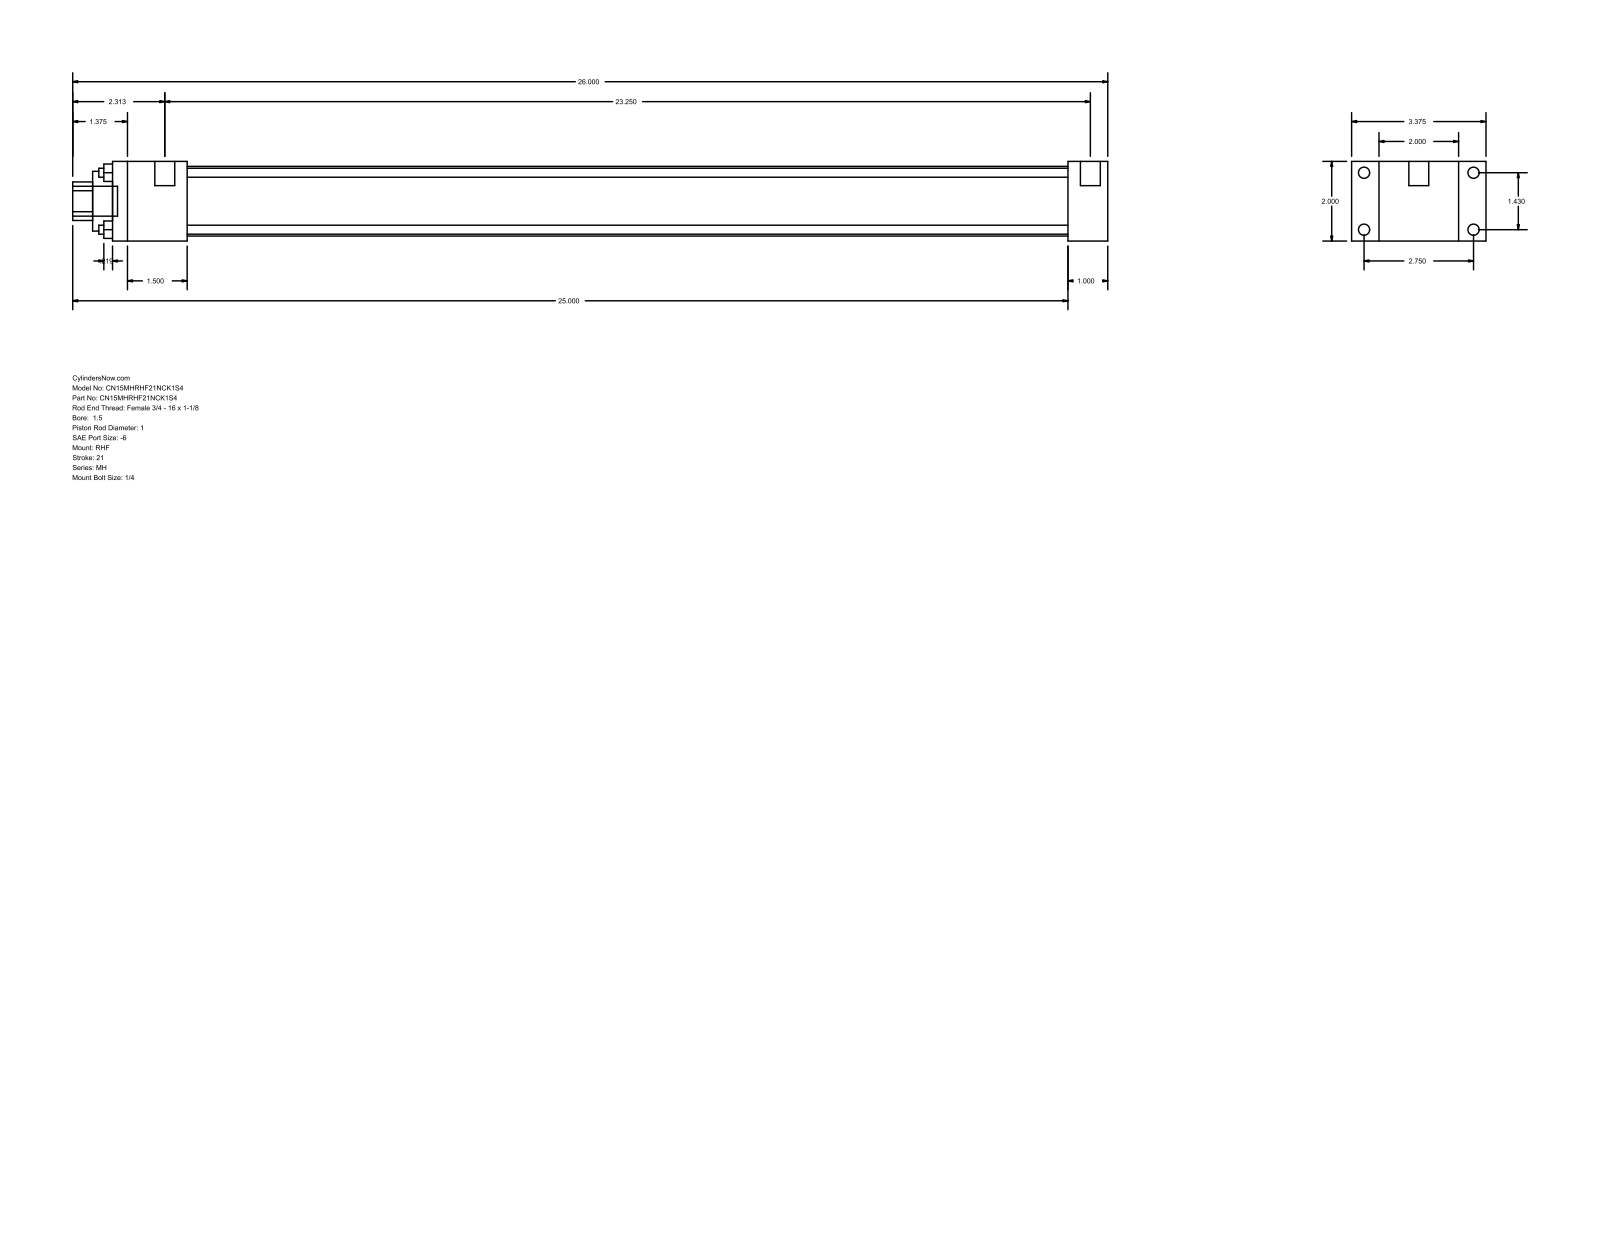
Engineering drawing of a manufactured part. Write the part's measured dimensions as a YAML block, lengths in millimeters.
part_name: "MH_RHF__0150_1"
step_written_by: "GSSL Pune (CONFIG_CONTROL_DESIGN)"
units: millimeters
bodies: {solids: 0, faces: 88, planar: 60, cylindrical: 28, other: 0}
overall_size: [660.4, 85.72, 50.8]
round_holes:
  - {diameter: 5.71, count: 4}
  - {diameter: 25.4, count: 1}
  - {diameter: 38.1, count: 1}
  - {diameter: 44.45, count: 1}
round_bosses_or_shafts:
  - {diameter: 7.14, count: 4}
  - {diameter: 5.56, count: 4}
  - {diameter: 12.7, count: 2}
  - {diameter: 19.05, count: 1}
partial_cylinders:
  - {radius: 12.29, count: 1}
face_to_face_distances: [50.8, 25.4, 17.46, 68.26, 85.72, 635, 609.6, 47.63, 561.97, 587.37]
hole_center_spacings: [25.68, 36.32, 51.36]
